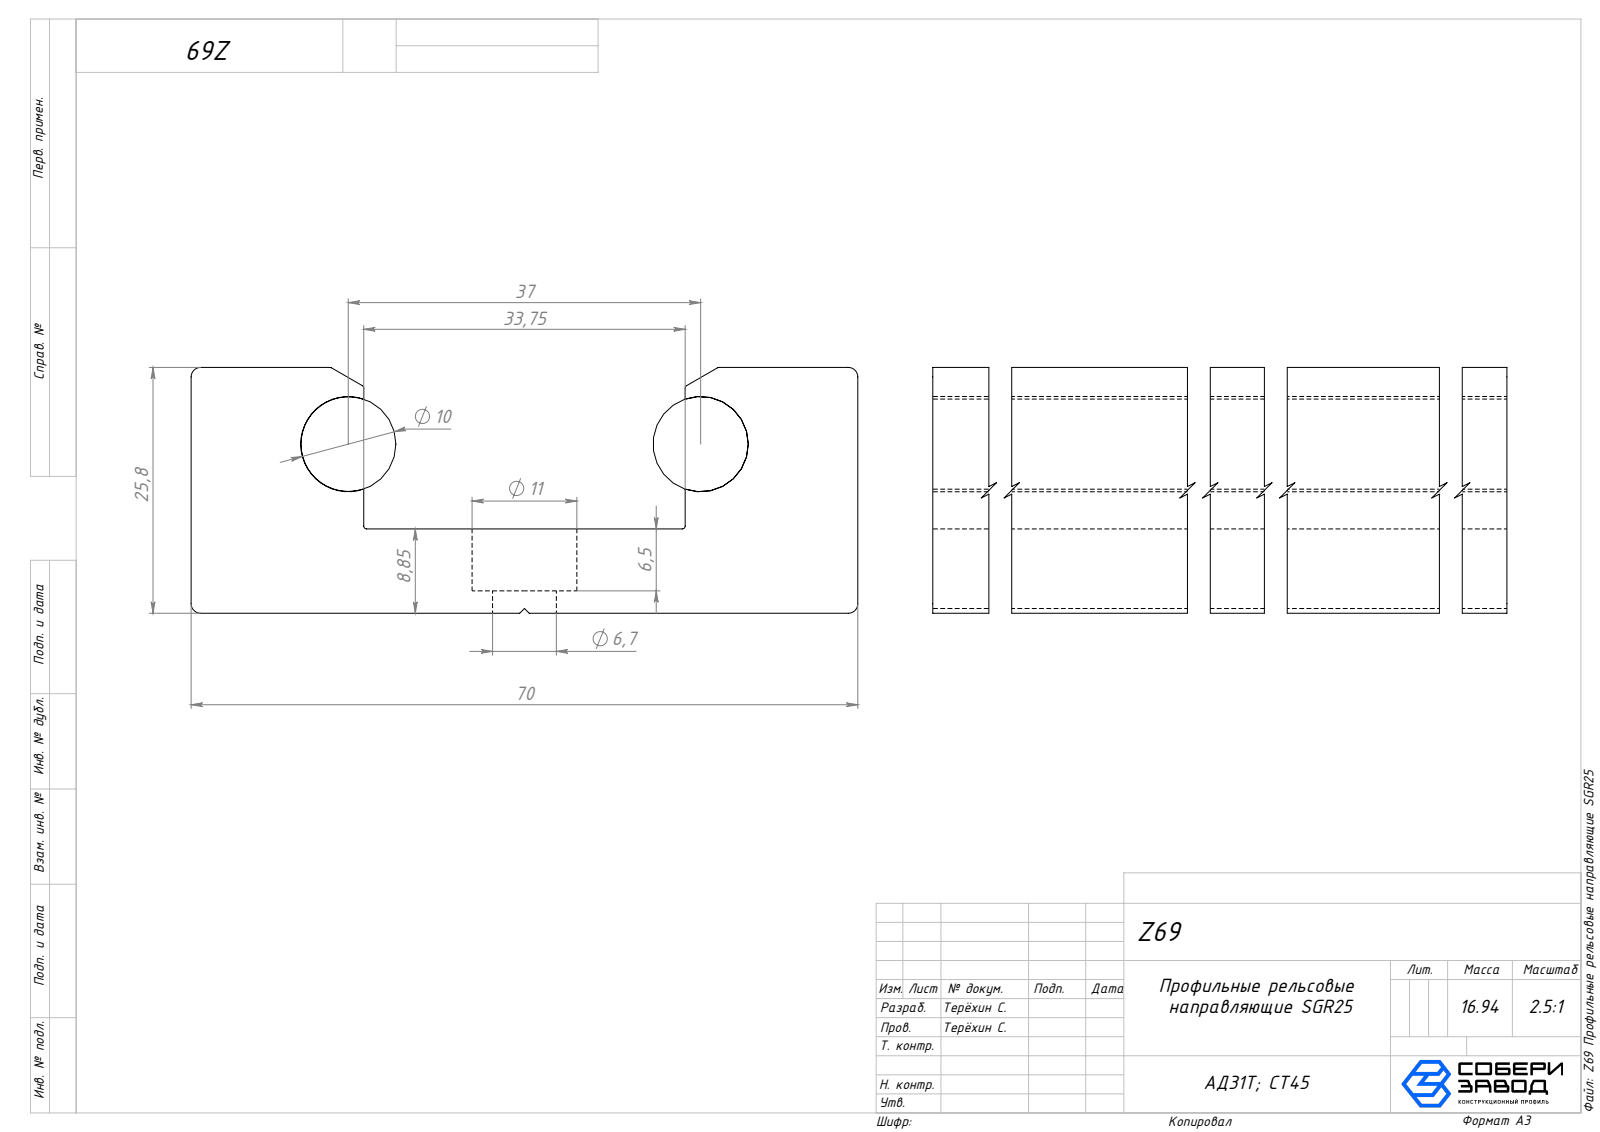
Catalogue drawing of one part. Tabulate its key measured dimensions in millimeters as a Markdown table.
| quantity | value |
| --- | --- |
| part name | Z69 Профильные рельсовые направляющие SGR25_00; Z69 Профильные рельсовые направляющие SGR25 |
| STEP written by | SolidWorks 2026 (CONFIG_CONTROL_DESIGN) |
| units | millimeters |
| bodies | 3 solids, 269 faces (120 planar, 149 cylindrical, 0 other) |
| overall size | 4000 × 70 × 25.8 |
| volume | 5 067 000 mm³ |
| surface area | 1 221 000 mm² |
| round holes (diameter × count) | 6.7 × 33, 11 × 33, 10 × 1 |
| round bosses / shafts (diameter × count) | 10 × 1 |
| partial cylindrical surfaces (radius × count) | 0.3 × 6, 1 × 4 |
| main face-to-face distances | 8.85, 25.8, 16.95, 70, 18.12, 51.88, 33.76, 2.35, 6.5, 23.45 |
| hole center spacings | 120, 240, 360, 480, 600, 720, 840, 960 |
